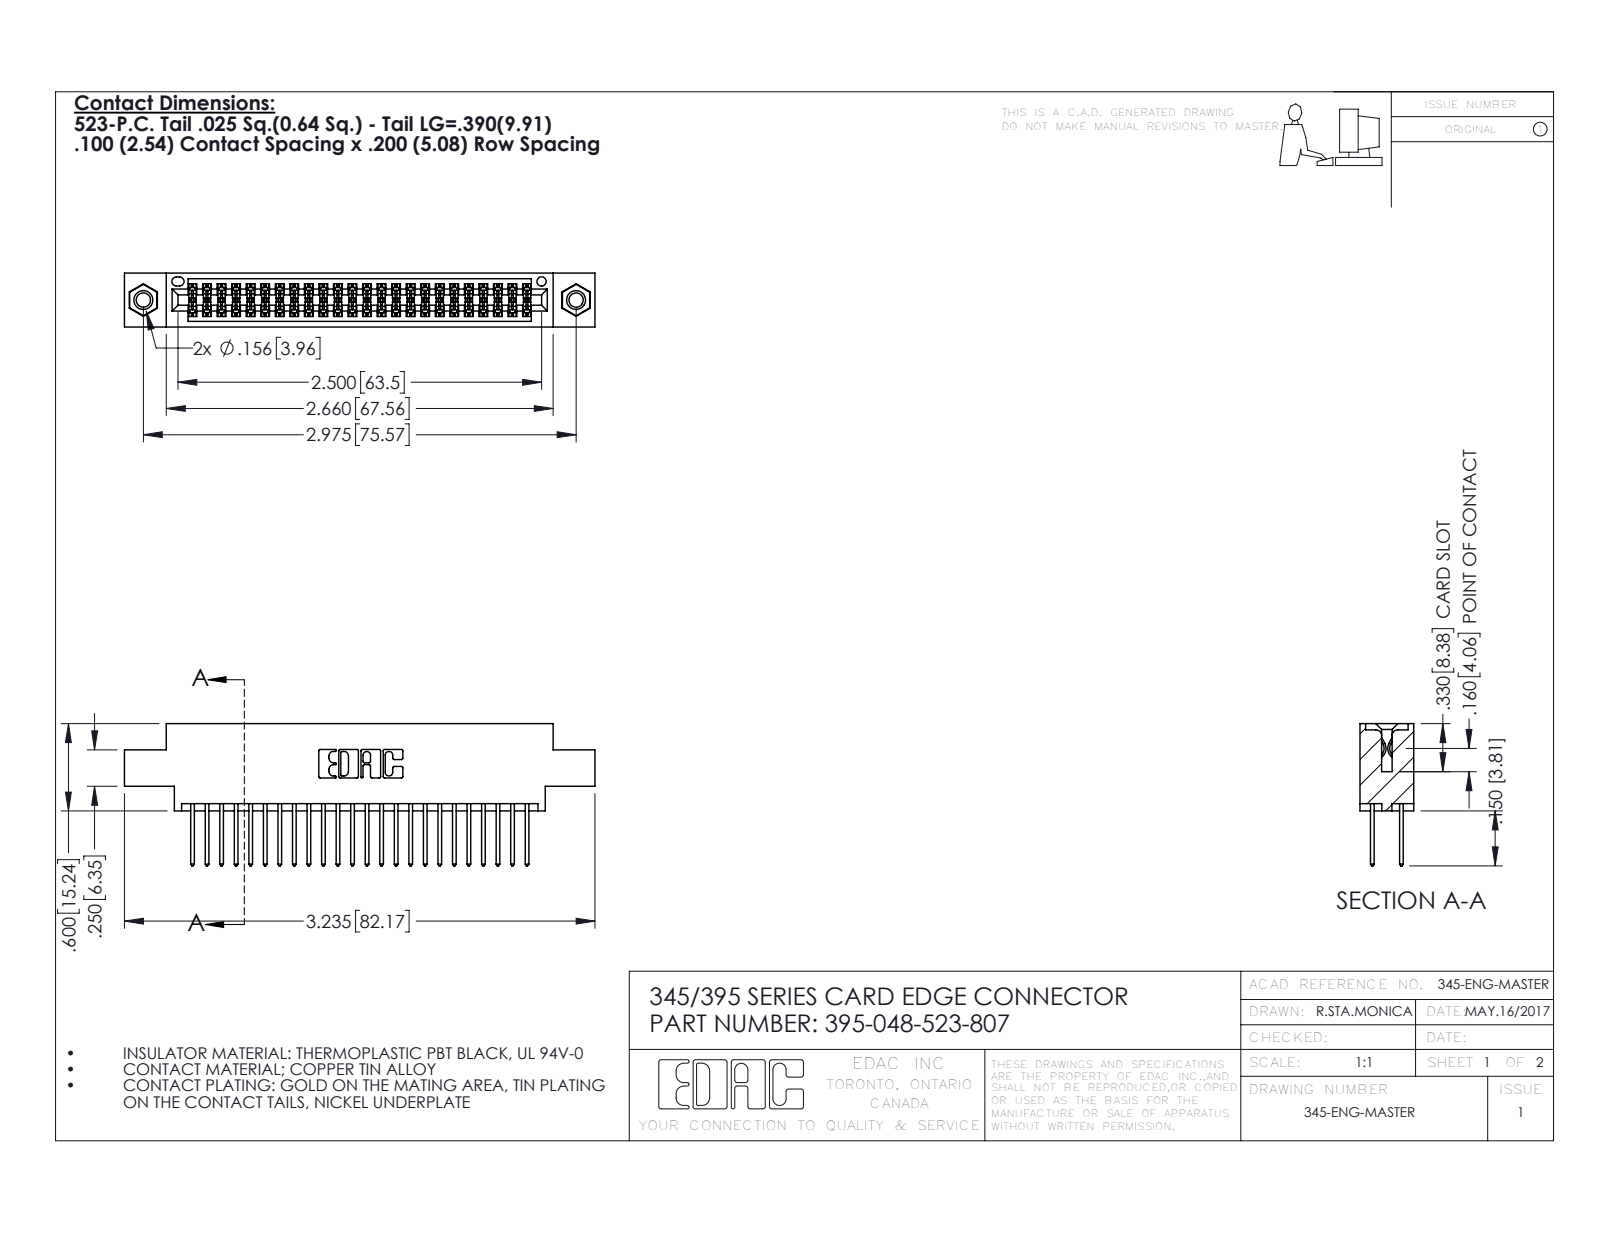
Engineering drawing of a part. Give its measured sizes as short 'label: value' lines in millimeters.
name: 345-250-001_345-250-005-103; 345 Part_0.170 Offset - 0.156 Dia-TI; 345-292-001_345-293-123; 395-048-523-807
written by: SolidWorks 2016 (CONFIG_CONTROL_DESIGN)
unit: mm
bodies: 51 solids, 2590 faces (1700 planar, 874 cylindrical, 16 other)
size: 82.2 × 24.8 × 9.4
volume: 7 780 mm³; area: 11 770 mm²
holes: 2× ⌀2.5, 2× ⌀3.2, 2× ⌀4, 1× ⌀1.6
bosses: 2× ⌀3.9
rounds: 72× R0.2, 48× R0.3, 22× R0.3, 6× R0.2, 6× R0.8, 3× R0.7, 2× R0.4, 2× R0.5
face distances: 1.8, 7.6, 5.1, 2.5, 6.9, 0.6, 9.4, 5.7, 4.4, 3.8
hole spacings: 6.9, 69.6, 75.6
